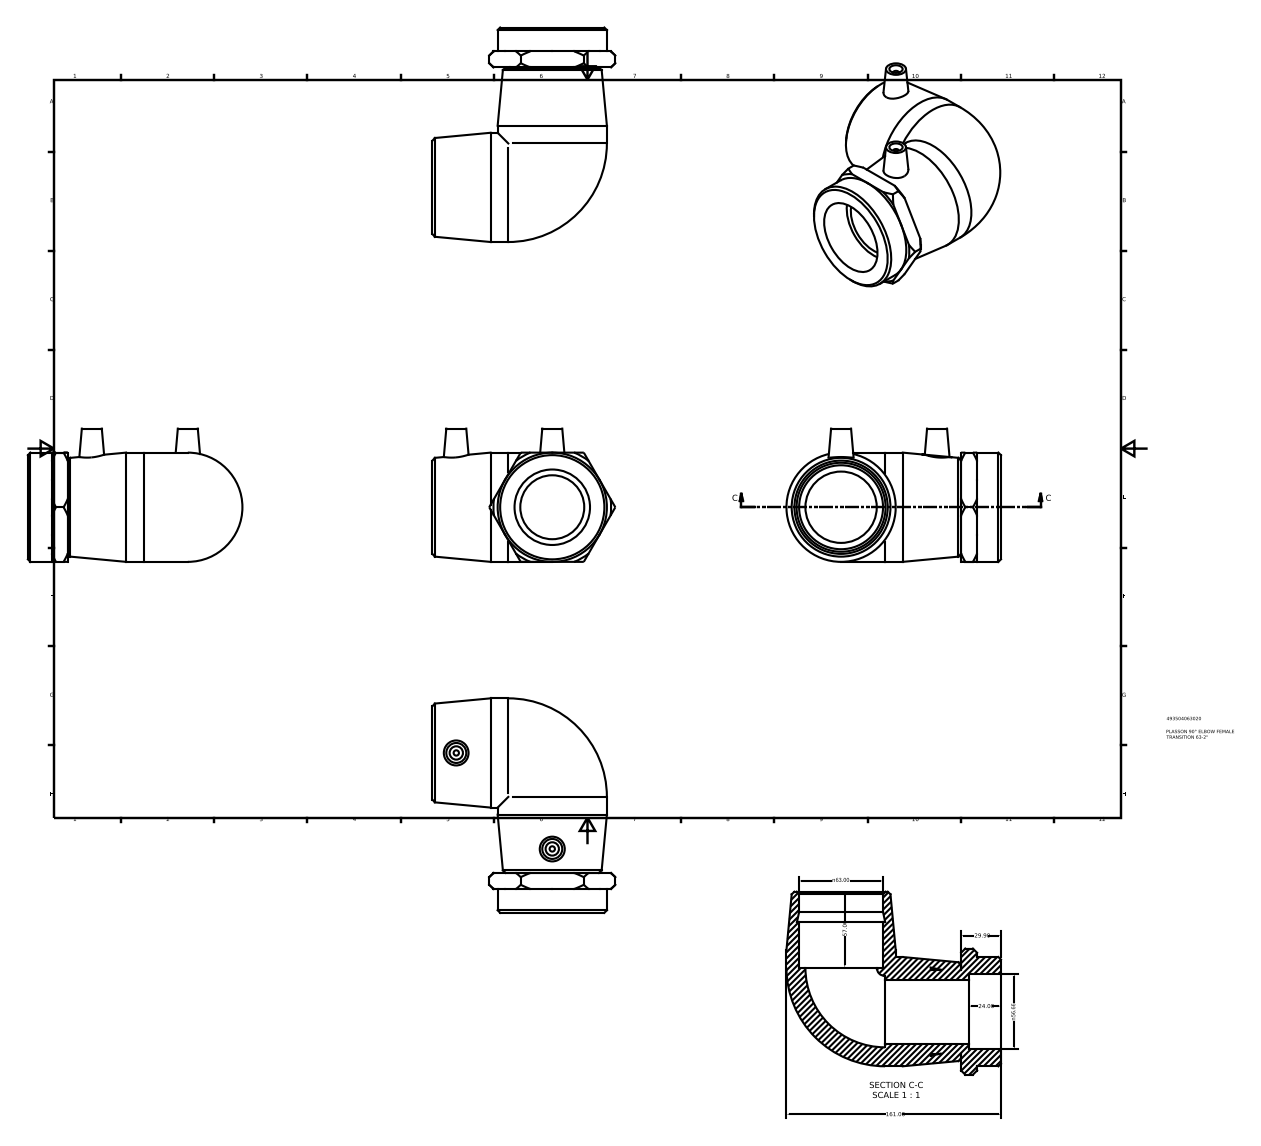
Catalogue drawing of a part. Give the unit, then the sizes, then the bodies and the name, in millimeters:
Units: millimetres
Overall size (bounding box): 161 × 137.34 × 100
Round holes (diameter × count): ⌀10 ×2, ⌀48 ×1, ⌀56.66 ×1, ⌀63 ×1
Round bosses / shafts (diameter × count): ⌀82 ×2, ⌀4 ×2, ⌀63 ×1
Main face-to-face distances: 29.9, 82, 57, 30, 6, 5.9, 24, 34.2, 22.8, 81.98
Hole centre spacings: 101.89
Volume: 533 126 mm³ · Surface area: 99 615 mm²
Bodies: 1 solid, 64 faces (27 planar, 13 cylindrical, 24 other)
Part name (STEP PRODUCT): 493504063020
STEP written by: Autodesk Inventor 2015 (AUTOMOTIVE_DESIGN)
